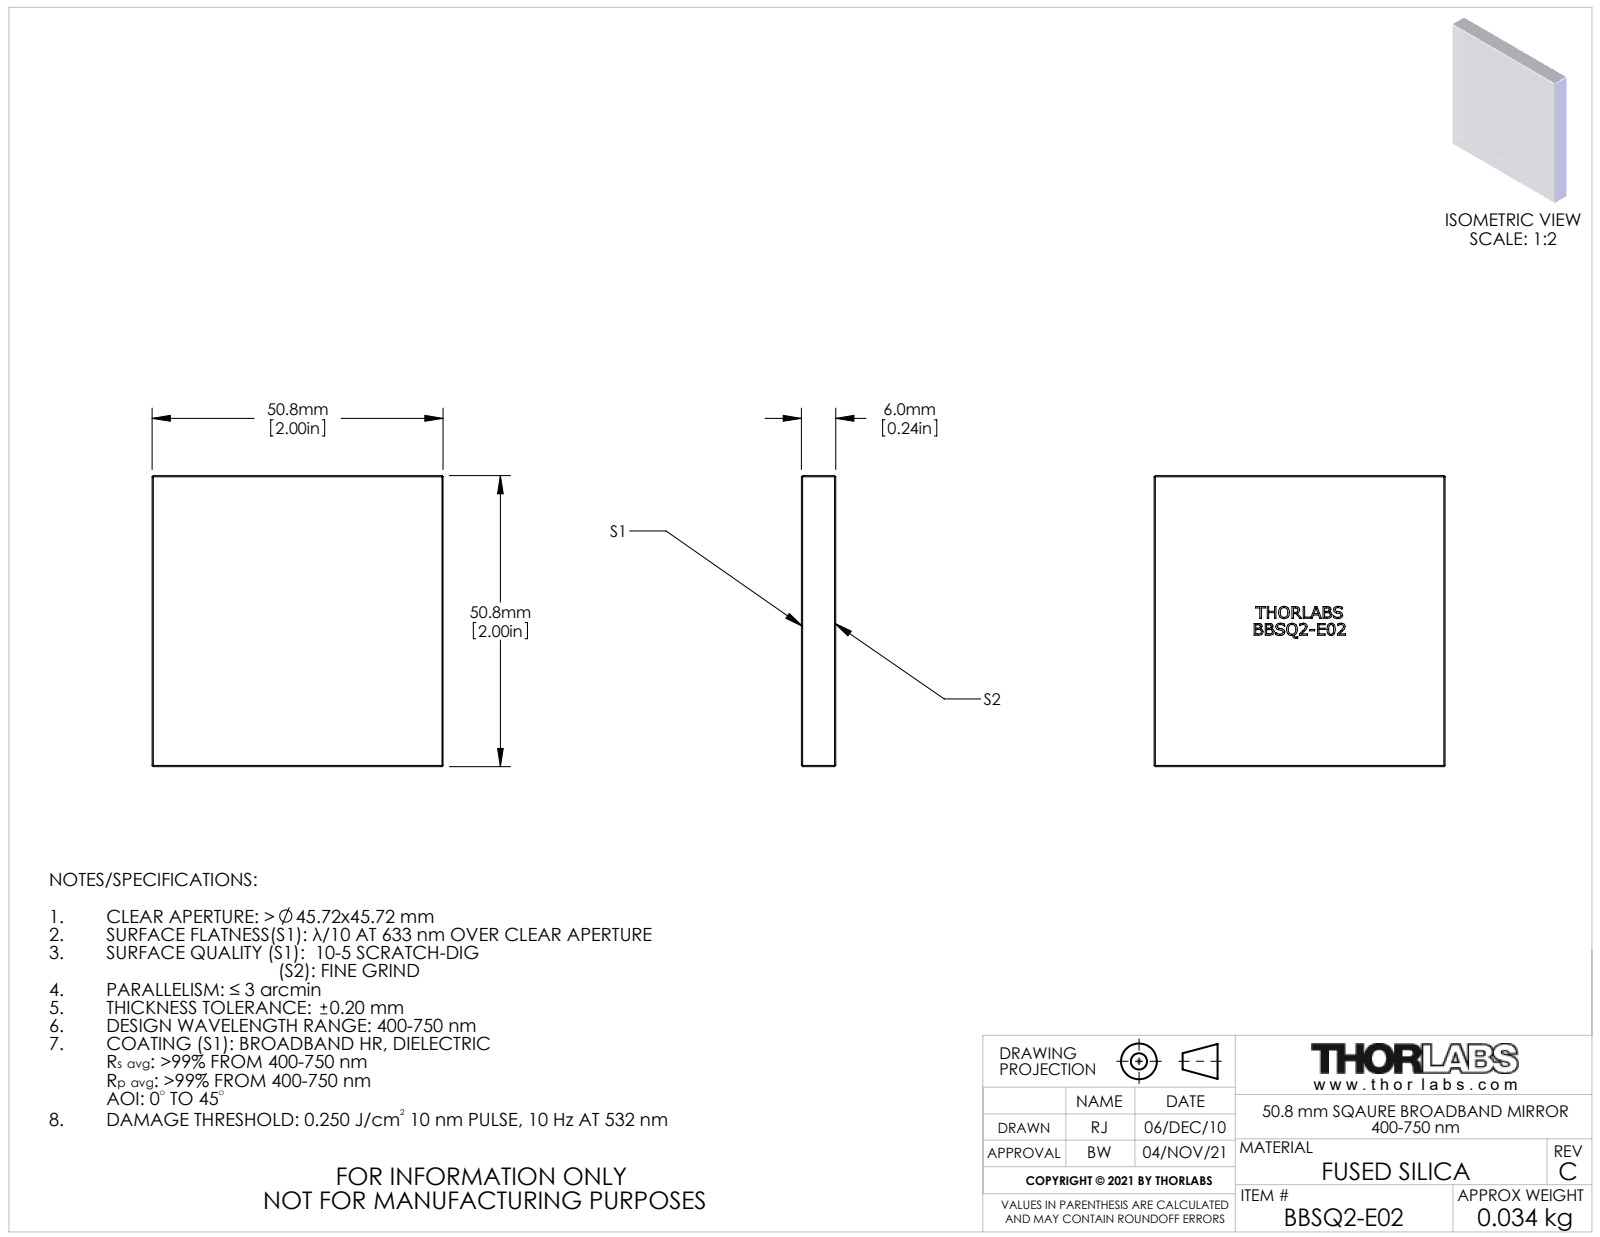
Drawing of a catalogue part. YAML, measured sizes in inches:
part_name: "21695-E0W"
step_written_by: "SolidWorks 2011 (AUTOMOTIVE_DESIGN)"
units: inches
bodies: {solids: 1, faces: 307, planar: 170, cylindrical: 0, other: 137}
overall_size: [2, 2, 0.236]
volume: 0.944
surface_area: 9.812
face_to_face_distances: [0.236, 2, 1.57, 1.57, 2.817, 2.426, 0.116, 0.072, 0.107, 0.081]
